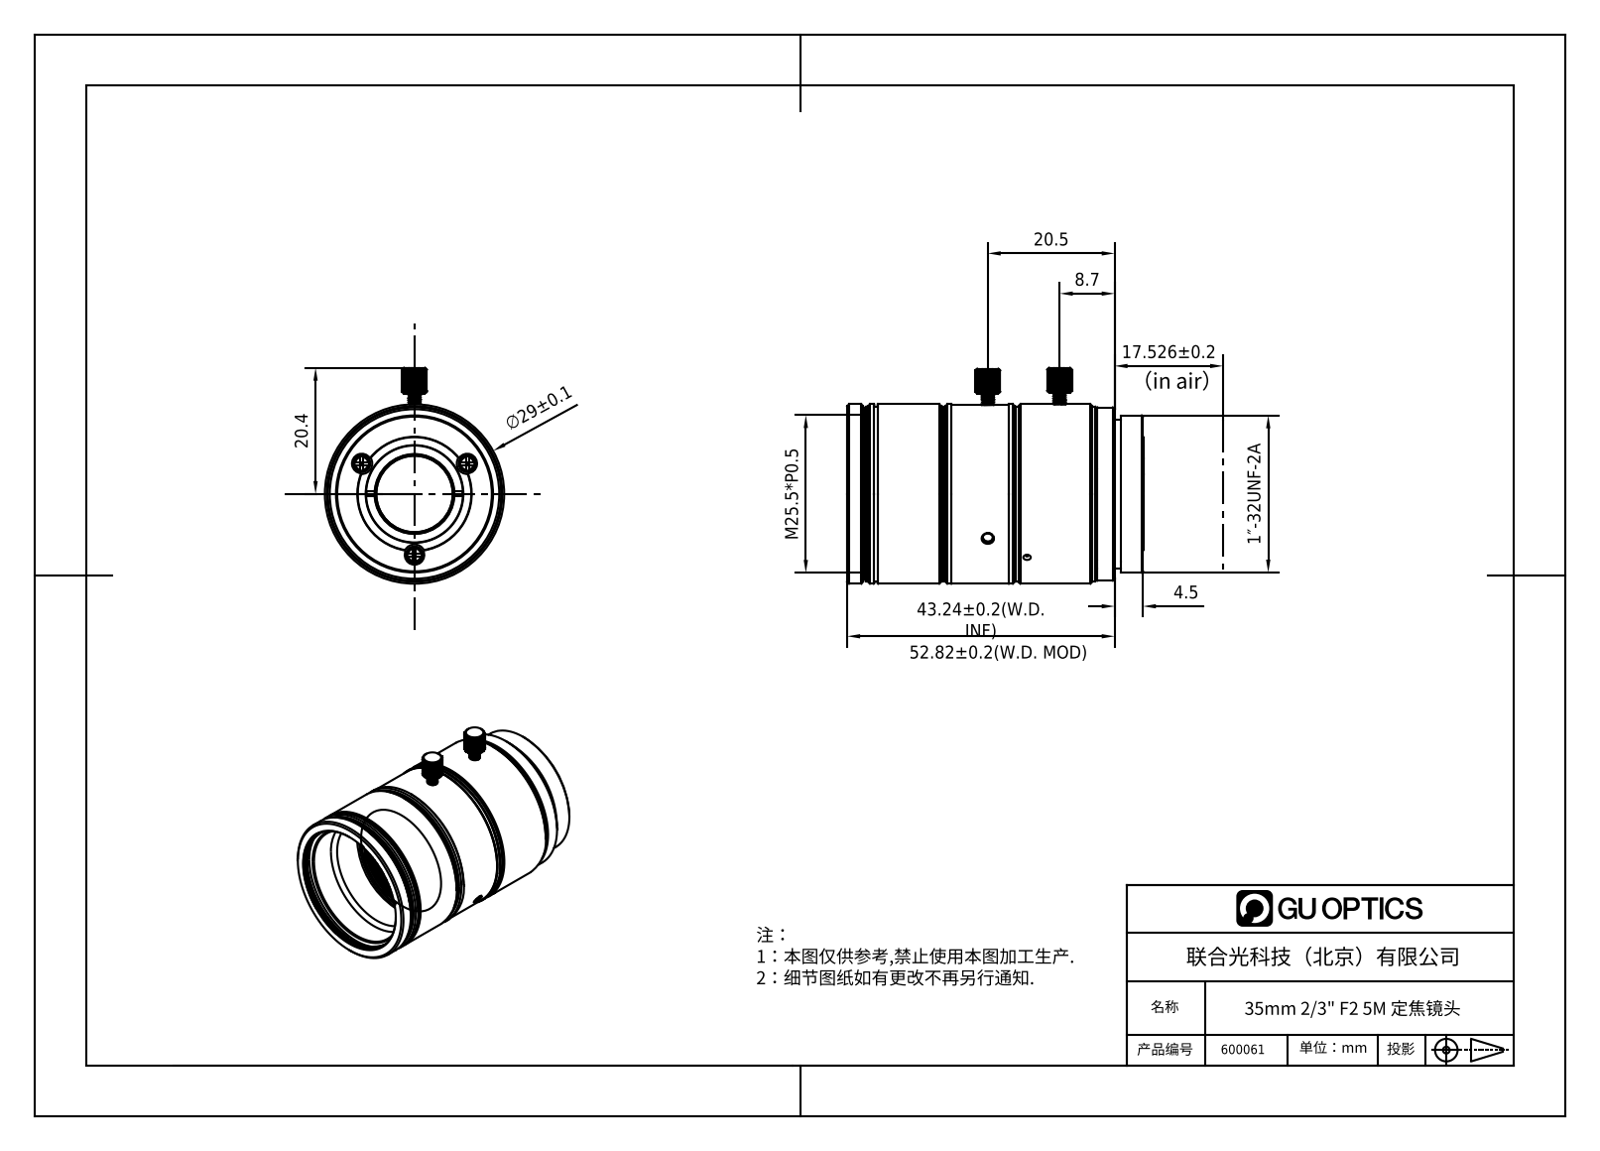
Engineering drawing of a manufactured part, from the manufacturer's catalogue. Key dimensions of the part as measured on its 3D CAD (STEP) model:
Part name (STEP PRODUCT): 600061
STEP written by: SolidWorks 2020 (CONFIG_CONTROL_DESIGN)
Units: millimetres
Bodies: 10 solids, 909 faces (251 planar, 422 cylindrical, 236 other)
Overall size (bounding box): 47.97 × 34.9 × 29
Volume: 23 917 mm³ · Surface area: 9 623 mm²
Round holes (diameter × count): ⌀1.6 ×5, ⌀2 ×4, ⌀1.7 ×3, ⌀2.8 ×3, ⌀12.82 ×1, ⌀14.2 ×1, ⌀15.5 ×1, ⌀17.5 ×1, ⌀17.57 ×1, ⌀18.43 ×1, ⌀18.89 ×1, ⌀21.16 ×1
Round bosses / shafts (diameter × count): ⌀1.6 ×5, ⌀2.5 ×3, ⌀1.2 ×3, ⌀2 ×2, ⌀29 ×1, ⌀28.8 ×1, ⌀28.2 ×1, ⌀28 ×1
Partial cylindrical surfaces — rounded edges, fillets, slot ends (radius × count): R3.39 ×6, R1.11 ×5, R3.43 ×4, R1.12 ×2, R2 ×2, R9.95 ×1, R10.05 ×1
Main face-to-face distances: 1.44, 7.85, 8, 6.41, 6.56, 3.15, 4.59, 3.26, 3.41, 47.84
Hole centre spacings: 9.85, 17.06
